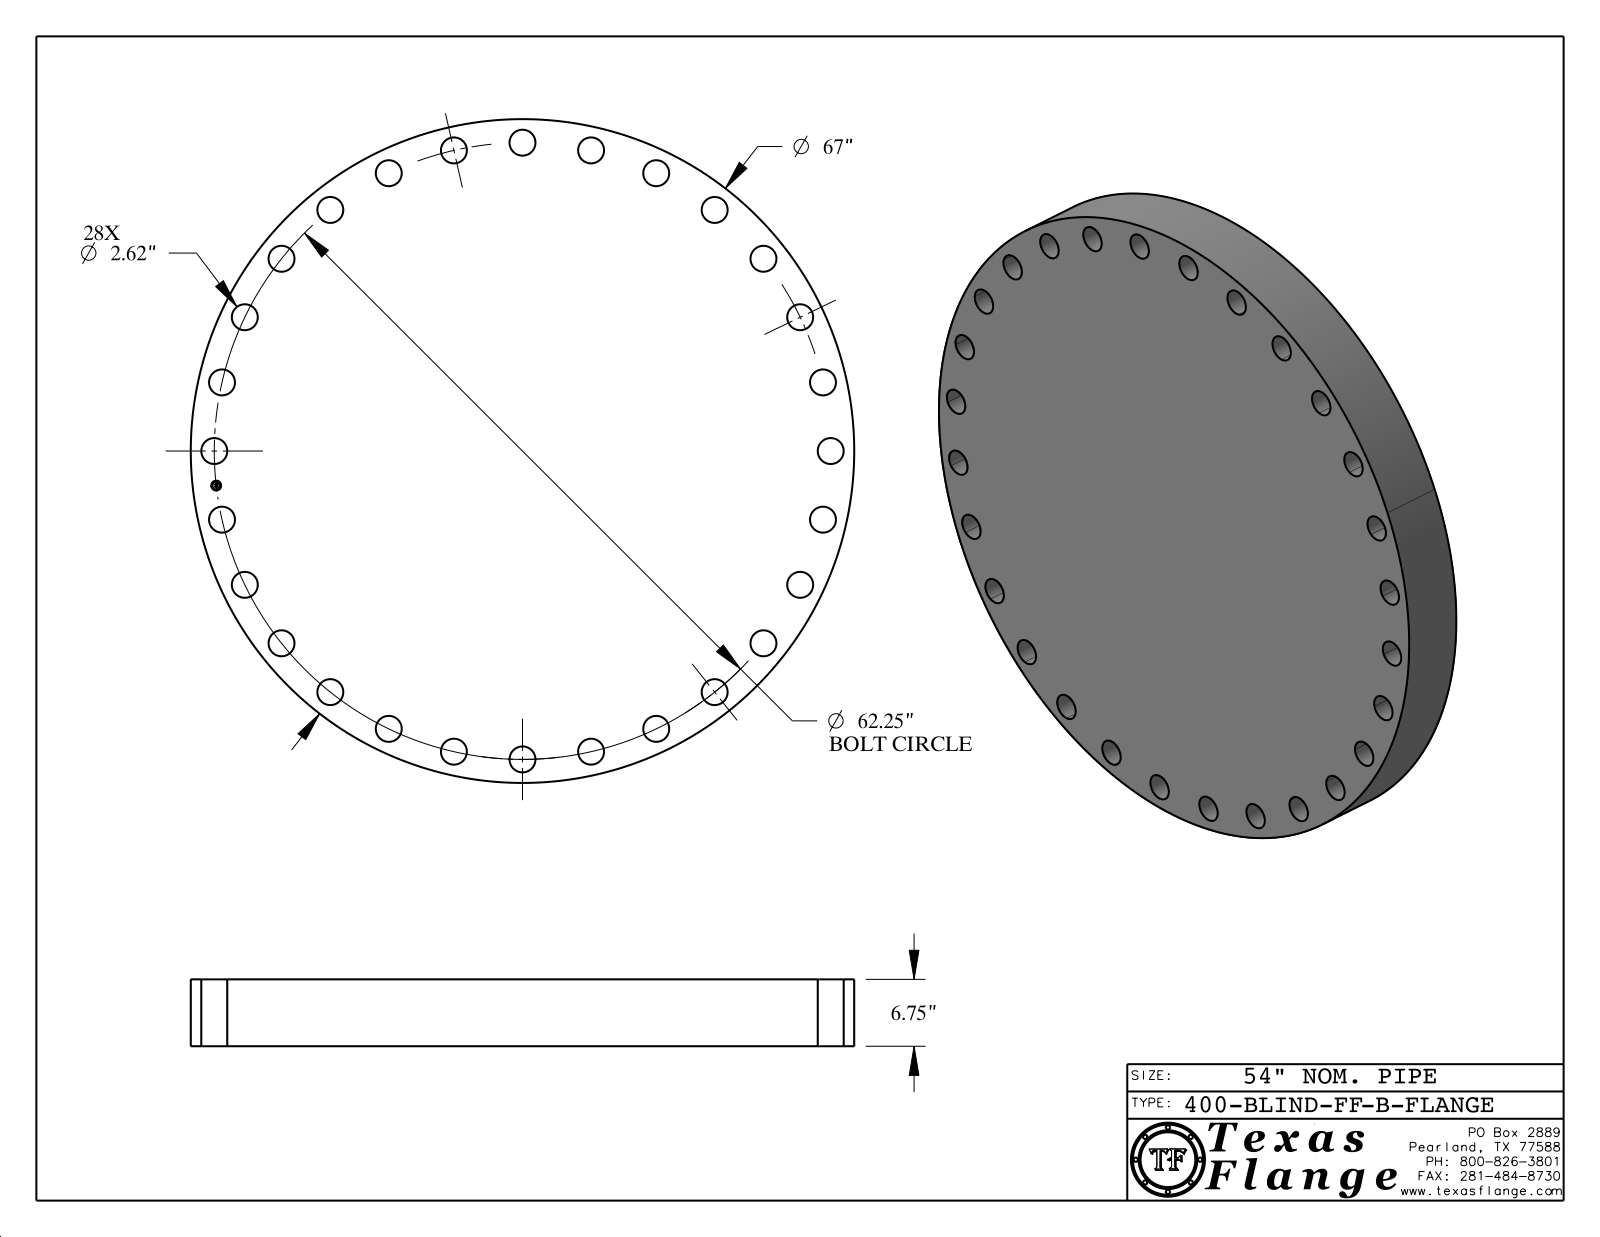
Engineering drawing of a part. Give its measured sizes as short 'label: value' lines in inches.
name: 400-BLIND-FF, Series B
written by: CATIA V5 STEP AP214 (AUTOMOTIVE_DESIGN)
unit: in
bodies: 1 solid, 445 faces (367 planar, 78 cylindrical, 0 other)
size: 67 × 67 × 6.75
volume: 22 779 in³; area: 9 726 in²
holes: 28× ⌀2.62, 1× ⌀1
bosses: 8× ⌀0.061, 1× ⌀67, 1× ⌀0.788
face distances: 6.75, 0.015, 6.735, 0.298, 0.293, 0.054, 0.193, 0.248, 0.044, 0.15
hole spacings: 6.97, 38.812, 48.669, 52.709, 60.689, 13.852, 27.009, 33.119
